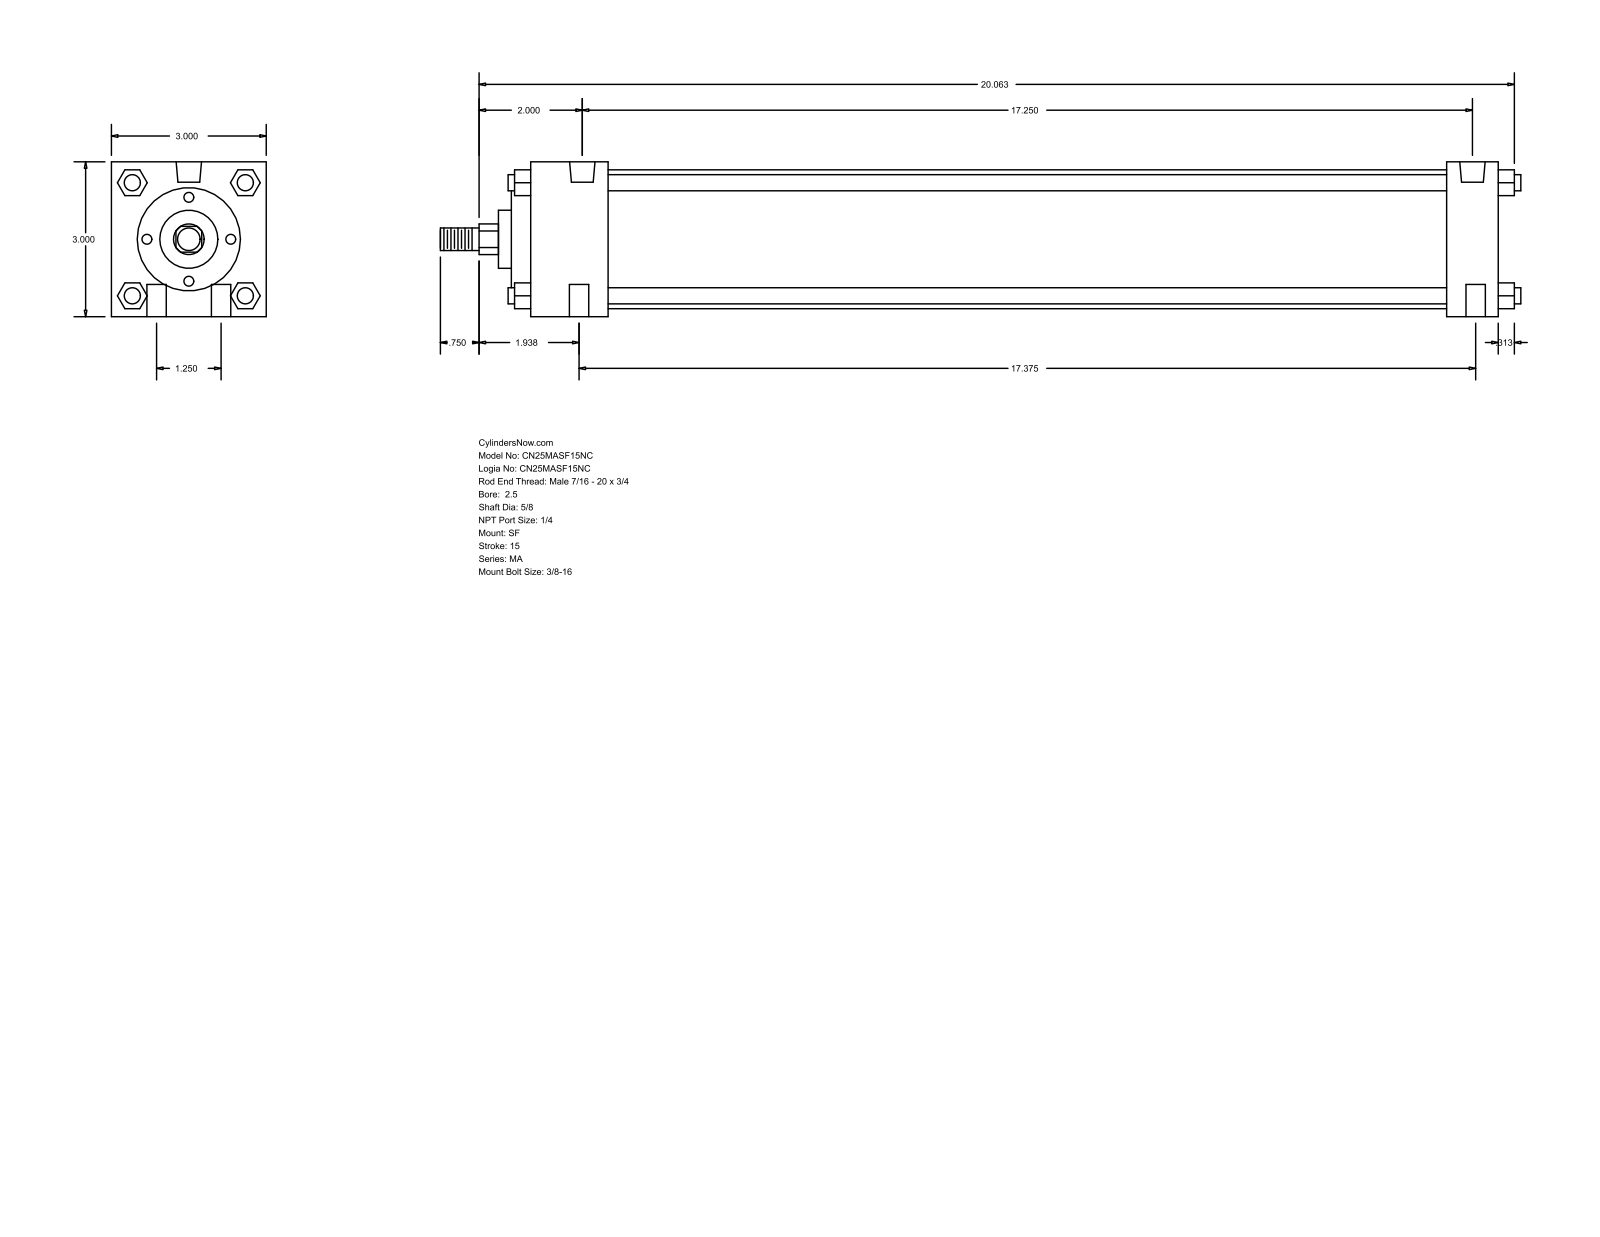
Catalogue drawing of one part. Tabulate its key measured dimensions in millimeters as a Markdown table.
| quantity | value |
| --- | --- |
| part name | MA_SF__0250_0.625 |
| STEP written by | GSSL Pune (CONFIG_CONTROL_DESIGN) |
| units | millimeters |
| bodies | 0 solids, 126 faces (95 planar, 31 cylindrical, 0 other) |
| overall size | 531.81 × 76.2 × 76.2 |
| round holes (diameter × count) | 9.53 × 4, 7.94 × 2, 12.49 × 2 |
| round bosses / shafts (diameter × count) | 7.94 × 4, 68.33 × 1, 50.8 × 1, 28.57 × 1, 15.88 × 1, 11.11 × 1 |
| partial cylindrical surfaces (radius × count) | 7.54 × 1 |
| main face-to-face distances | 76.2, 476.25, 25.4, 450.85, 38.1, 412.75, 438.15, 12.7, 9.52, 47.62 |
| hole center spacings | 15.96, 440.03, 31.76, 438.15, 441.33, 442.47 |
